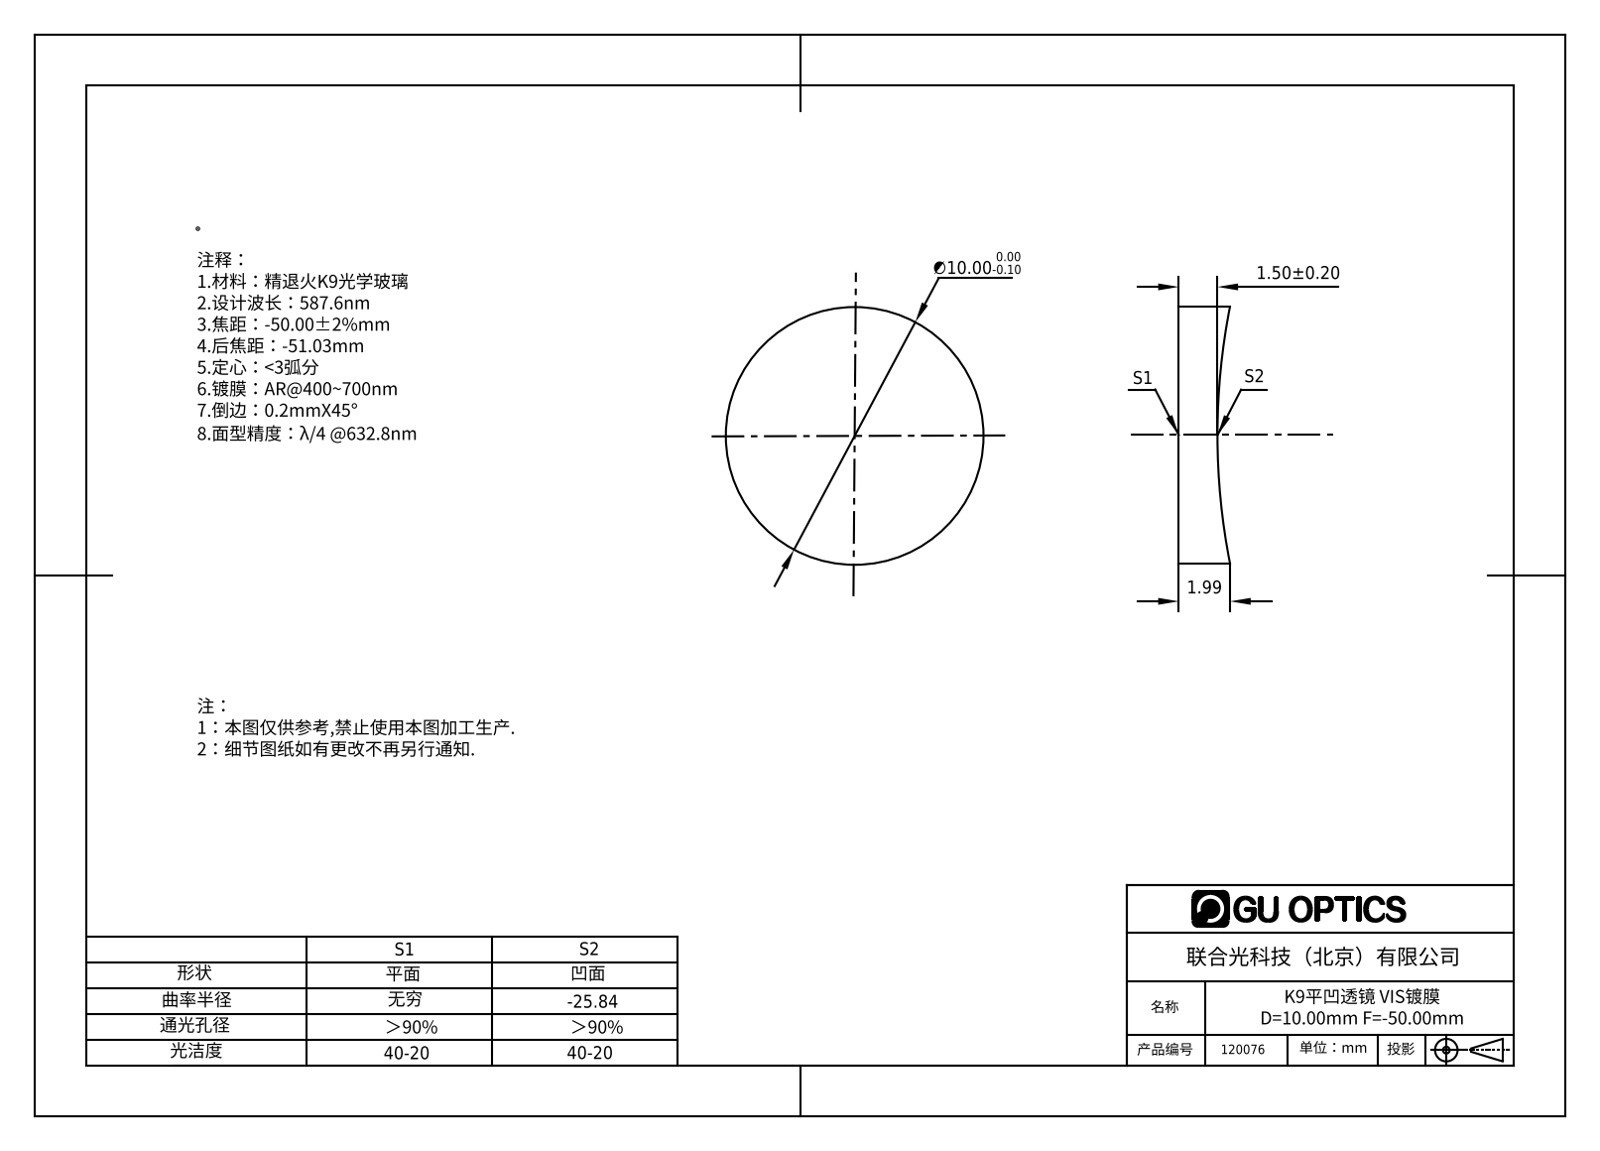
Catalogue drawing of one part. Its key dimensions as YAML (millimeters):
part_name: "120016"
step_written_by: "SolidWorks 2016 (AUTOMOTIVE_DESIGN)"
units: millimeters
bodies: {solids: 1, faces: 5, planar: 1, cylindrical: 2, other: 2}
overall_size: [10, 10, 1.99]
volume: 137
surface_area: 220
round_bosses_or_shafts:
  - {diameter: 10, count: 1}
